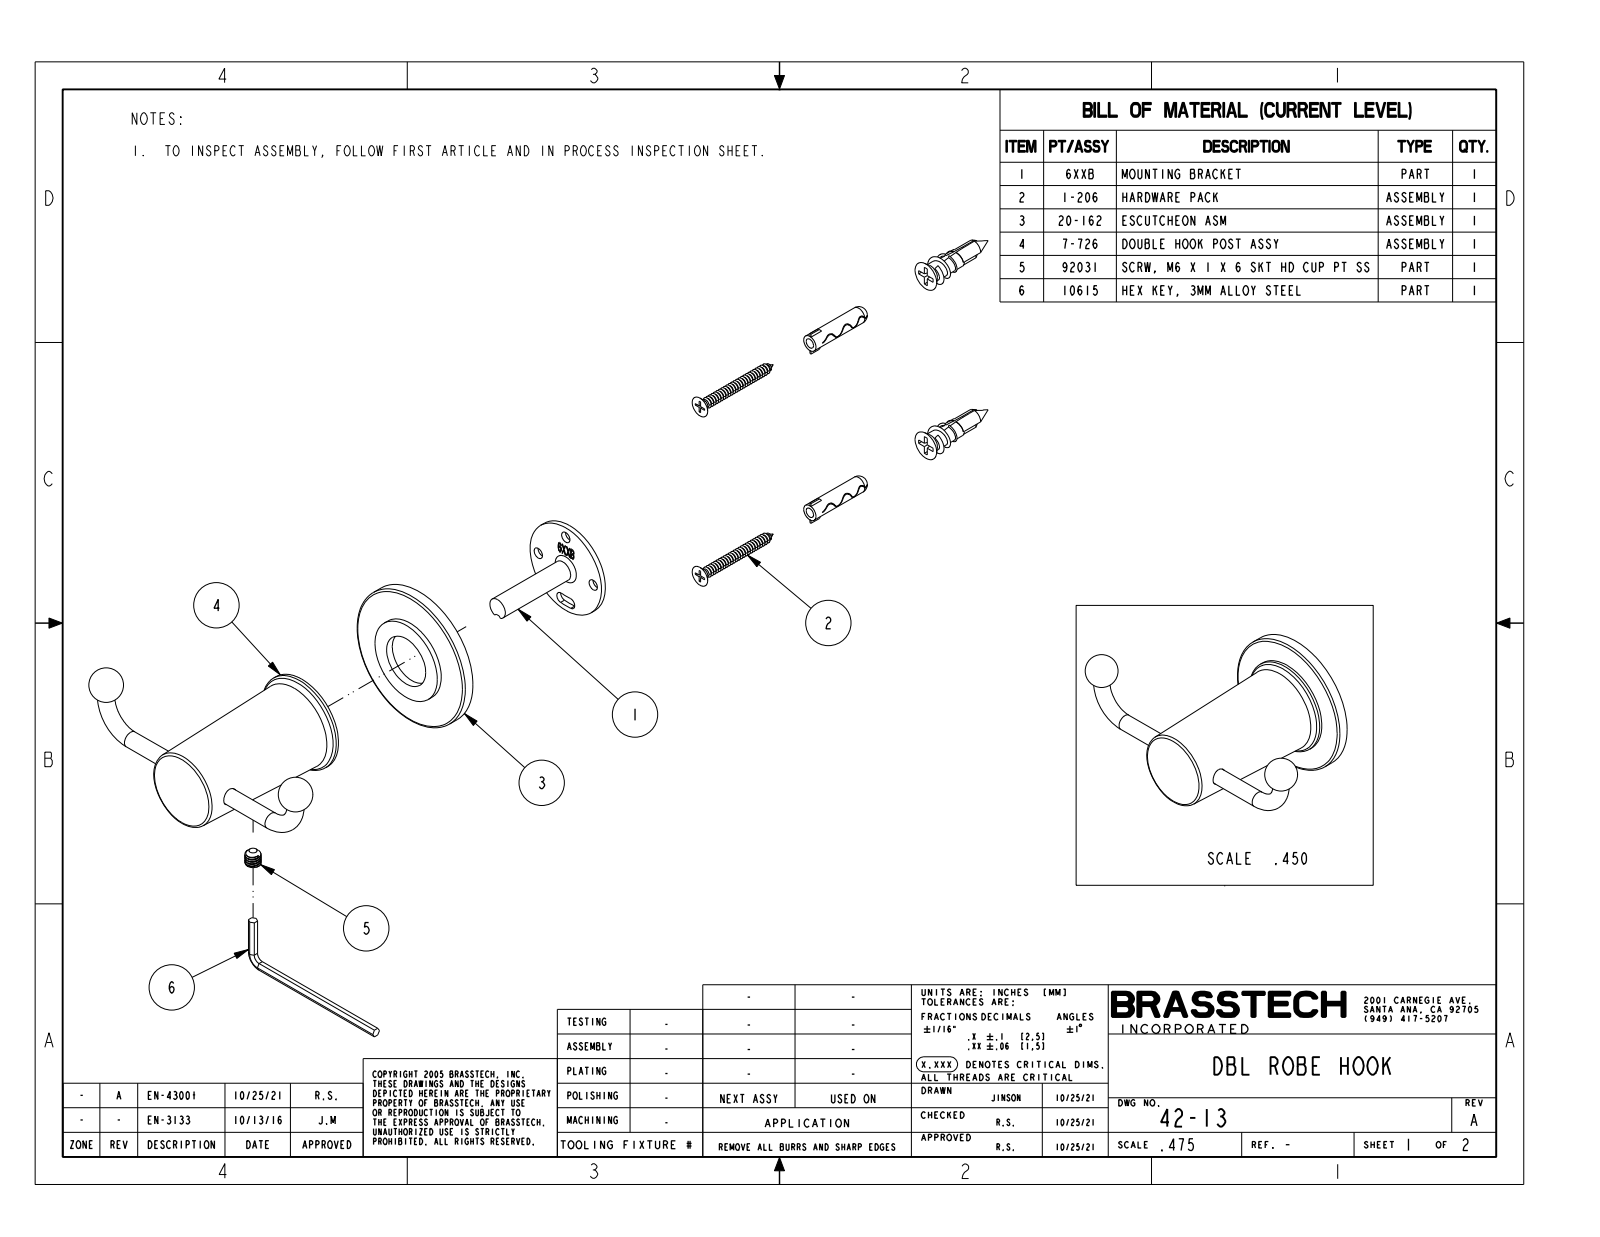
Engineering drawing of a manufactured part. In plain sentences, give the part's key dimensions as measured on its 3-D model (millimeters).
The part is named "42-13". Its 3-D file was written by "CREO PARAMETRIC BY PTC INC, 2018400 (CONFIG_CONTROL_DESIGN)". It is 1 solid with 34 faces: 6 planar, 10 cylindrical and 18 other. Overall it measures 111.2 by 67.5 by 55.9 millimeters. Its volume is 67 730 cubic millimeters and its surface area 14 840 square millimeters. Round bosses or shafts: 1 of diameter 55.9, 1 of diameter 38.1, 1 of diameter 32.4, 1 of diameter 6.4. The main face-to-face distances are 4.7, 67.5, 62.7, 5, 62.5.
